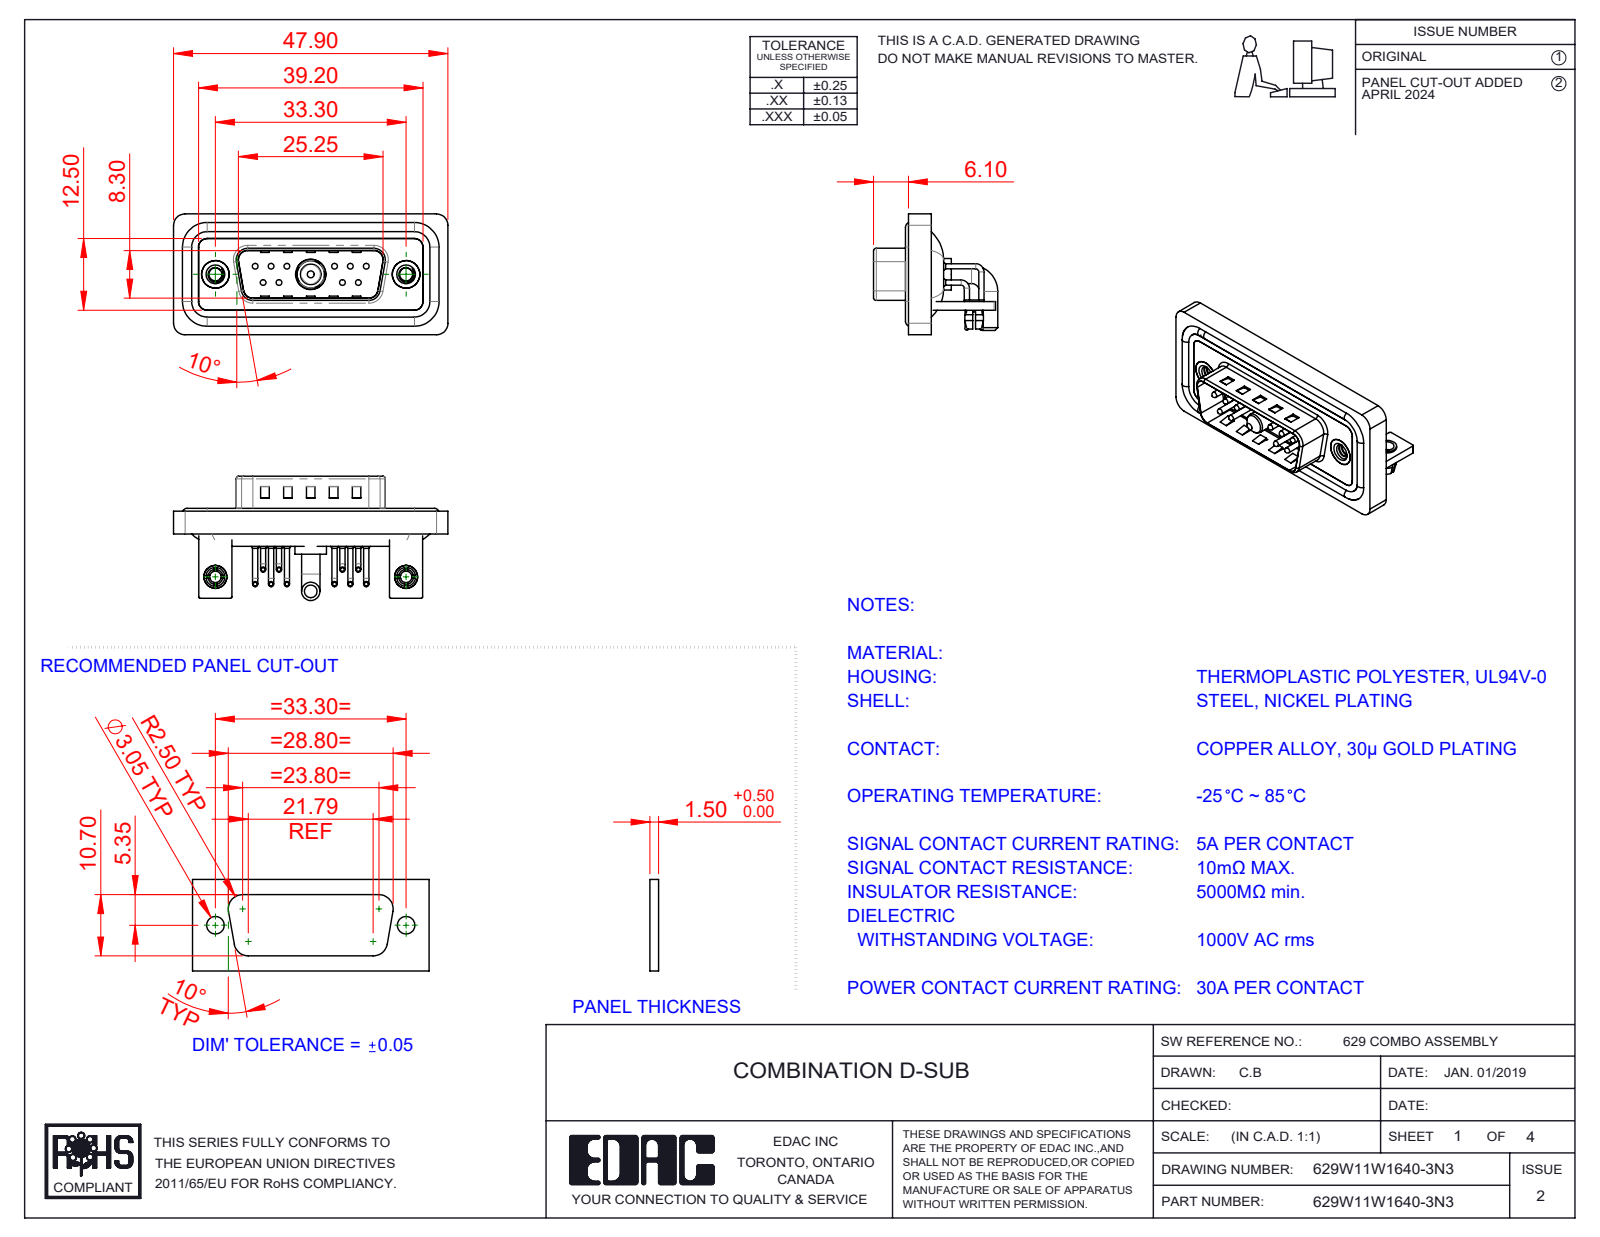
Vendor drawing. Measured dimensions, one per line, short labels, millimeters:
name: 629Combo Contact Row 2; 629Combo Board Lock; 629Combo Stabilizer Bracket; 629Combo Shell Rear_15 Contacts (+7 more)
written by: SolidWorks 2023 (CONFIG_CONTROL_DESIGN)
unit: mm
bodies: 23 solids, 1735 faces (904 planar, 619 cylindrical, 212 other)
size: 47.9 × 21.7 × 21.1
volume: 5 931 mm³; area: 10 096 mm²
holes: 12× ⌀2, 10× ⌀0.75, 10× ⌀1.6, 2× ⌀2.26, 2× ⌀2.5, 2× ⌀3.2, 2× ⌀4, 2× ⌀4.8, 2× ⌀5, 1× ⌀4.85, 1× ⌀5.3
bosses: 20× ⌀0.9, 10× ⌀1.5, 10× ⌀1, 10× ⌀0.65, 4× ⌀1.6, 2× ⌀4.9, 2× ⌀4, 2× ⌀3.4
rounds: 21× R2, 18× R1.5, 16× R0.25, 10× R1.01, 9× R0.5, 8× R1.6, 7× R1, 4× R0.6
face distances: 0.4, 0.8, 1.5, 2.9, 2.1, 1.1, 1.6, 1.2, 3.7, 4.1
hole spacings: 3.16, 2.77, 13.85, 11.08, 16.62, 5.03, 5.04, 5.54
